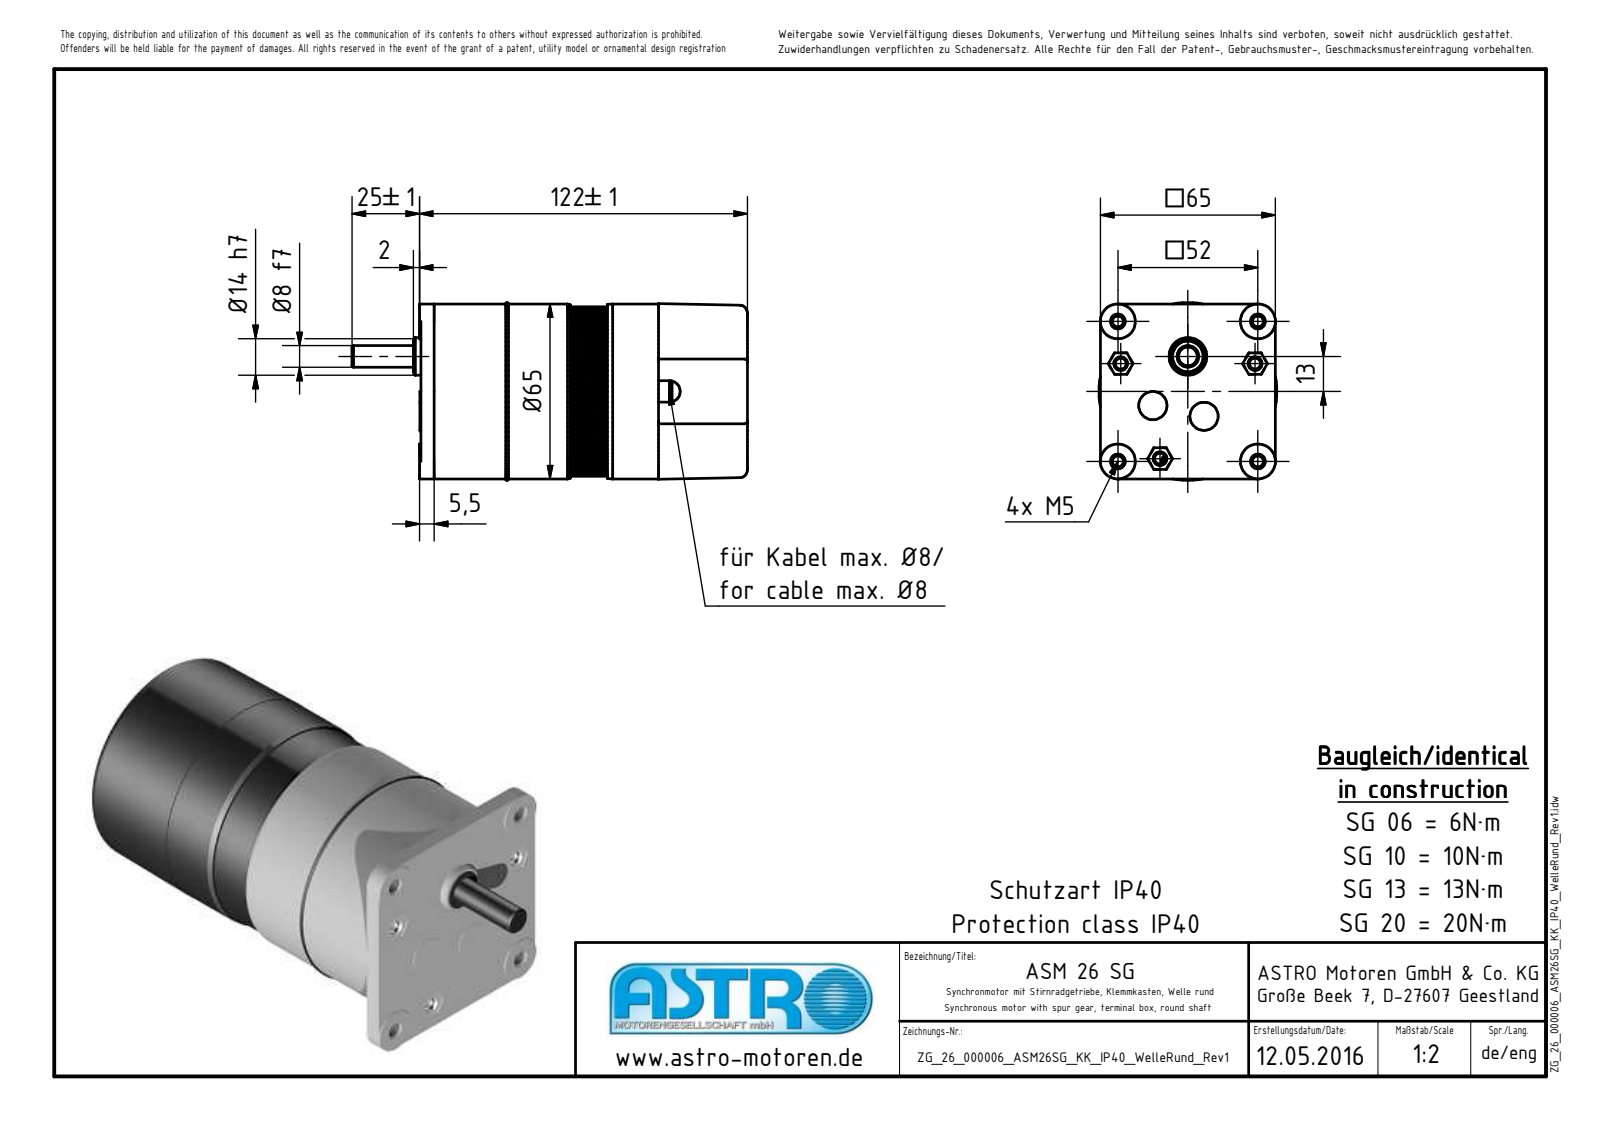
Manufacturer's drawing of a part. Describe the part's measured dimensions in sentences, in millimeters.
The part is named "ZG_26_000006_ASM26SG_KK_IP40_WelleRund_Rev1; 5101-STG-Metall; LagerschaleB3-ZG-Rev1-0; ZG_51108x067_Endwelle_8x67_Rev0 (+6 more)". Its 3-D file was written by "Autodesk Inventor 2010 (AUTOMOTIVE_DESIGN)". It is 14 solids with 458 faces: 181 planar, 90 cylindrical and 187 other. Overall it measures 146.8 by 66 by 66 millimeters. Its volume is 168 435 cubic millimeters and its surface area 84 945 square millimeters. Round holes: 8 of diameter 4.1, 3 of diameter 5.2, 2 of diameter 12, 1 of diameter 4.3, 1 of diameter 6, 1 of diameter 8, 1 of diameter 8.5, 1 of diameter 15.5, 1 of diameter 16, 1 of diameter 59, 1 of diameter 63. Round bosses or shafts: 4 of diameter 13, 4 of diameter 4, 4 of diameter 3.62, 2 of diameter 12.01, 2 of diameter 10.5, 2 of diameter 8.5, 2 of diameter 3, 2 of diameter 2.5. Partial cylindrical surfaces (rounded edges, fillets, slot ends): 16 of radius 0.5, 5 of radius 1, 4 of radius 5.26, 1 of radius 4. The main face-to-face distances are 47.5, 52.5, 19.5, 67, 5, 72, 88.3, 83.3, 35.8, 16.3. The hole center spacings are 27, 49.89, 20.66, 38.18, 44.9, 52.96, 10.53, 10.54.
